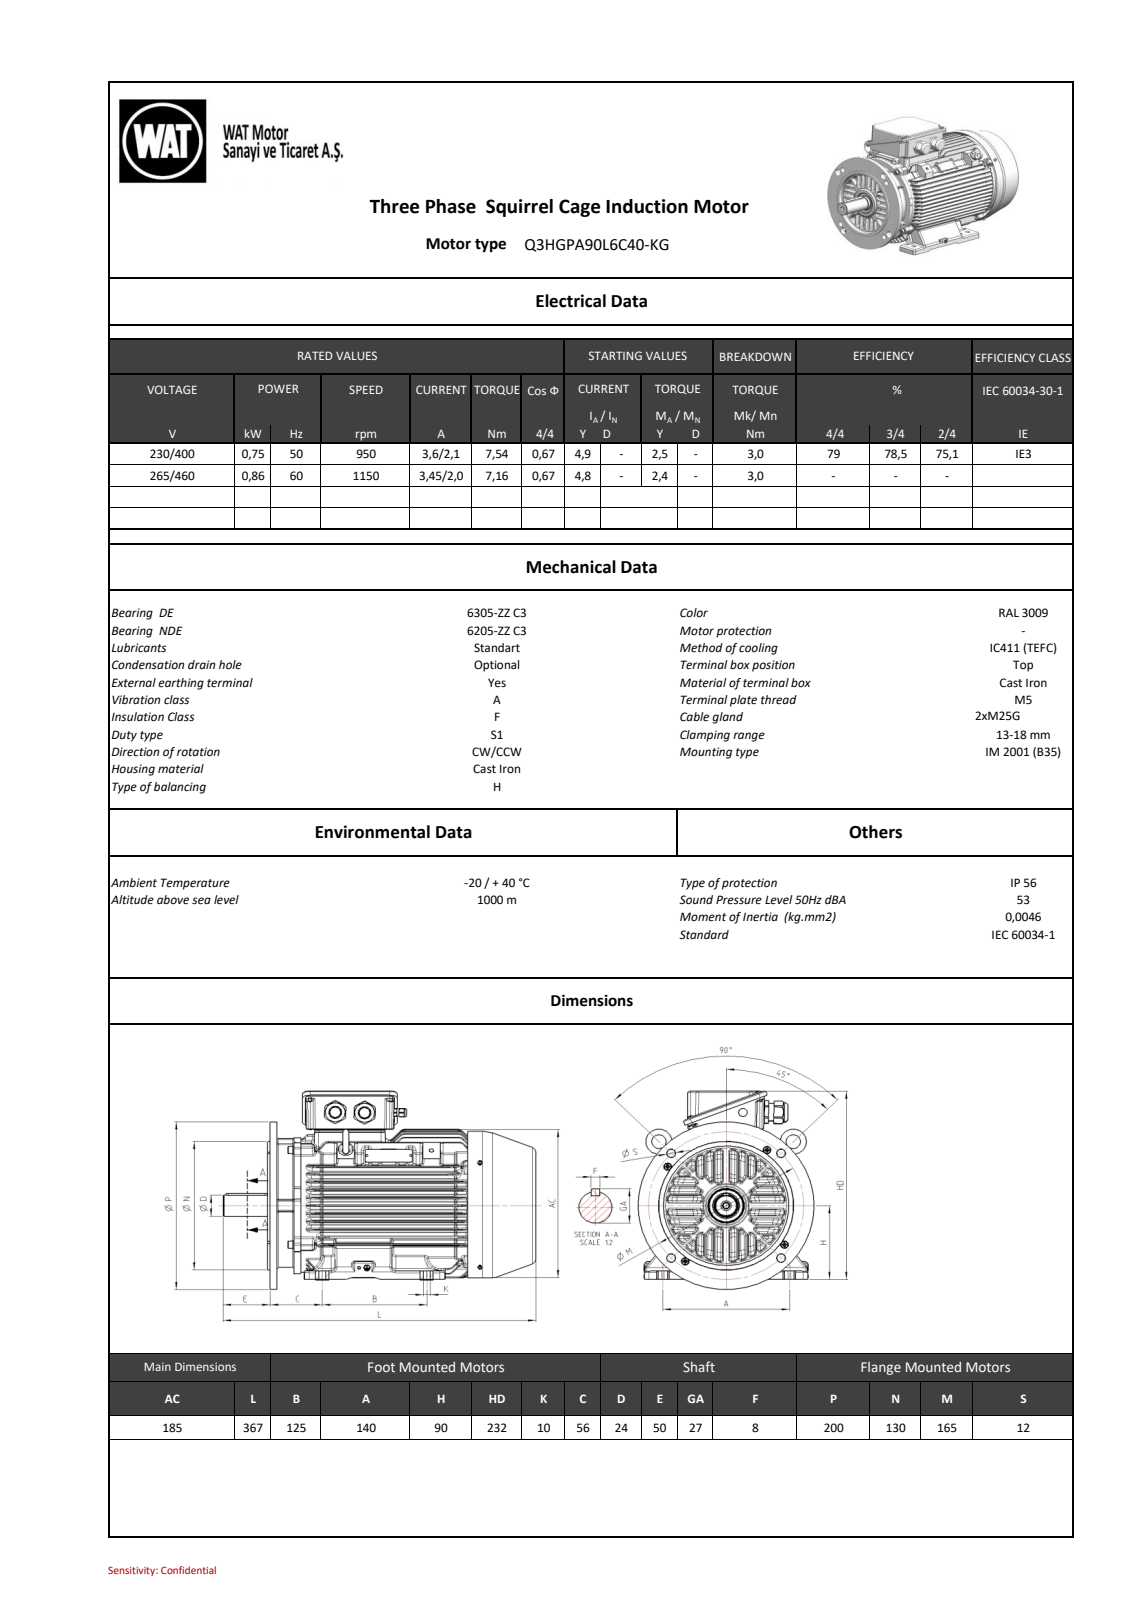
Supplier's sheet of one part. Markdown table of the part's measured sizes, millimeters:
| quantity | value |
| --- | --- |
| part name | 26000A30F4D8roa6 |
| STEP written by | SIEMENS PLM Software NX 11.0 (AUTOMOTIVE_DESIGN) |
| units | millimeters |
| bodies | 0 solids, 3207 faces (872 planar, 905 cylindrical, 1430 other) |
| overall size | 368.42 × 241.98 × 226.53 |
| round holes (diameter × count) | 10 × 6, 13.5 × 4, 4.2 × 3, 2.5 × 2, 17.2 × 2, 6.5 × 1, 6.8 × 1, 8.4 × 1, 36.9 × 1, 37.1 × 1, 174 × 1 |
| round bosses / shafts (diameter × count) | 20 × 4, 8.65 × 3, 8 × 3, 5 × 3, 27.7 × 2, 25.25 × 2, 200 × 1, 176 × 1 |
| partial cylindrical surfaces (radius × count) | 1.5 × 308, 2 × 52, 1 × 34, 3 × 32, 4 × 32, 5 × 24, 1.2 × 21, 26.5 × 12 |
| main face-to-face distances | 12.04, 6.45, 262.18, 268.63, 49.79, 311.97, 318.42, 62.58, 3, 3.01 |
| hole center spacings | 116.67, 80.5, 139.43, 21.36, 82.5, 99.24, 129.32, 150.59 |
